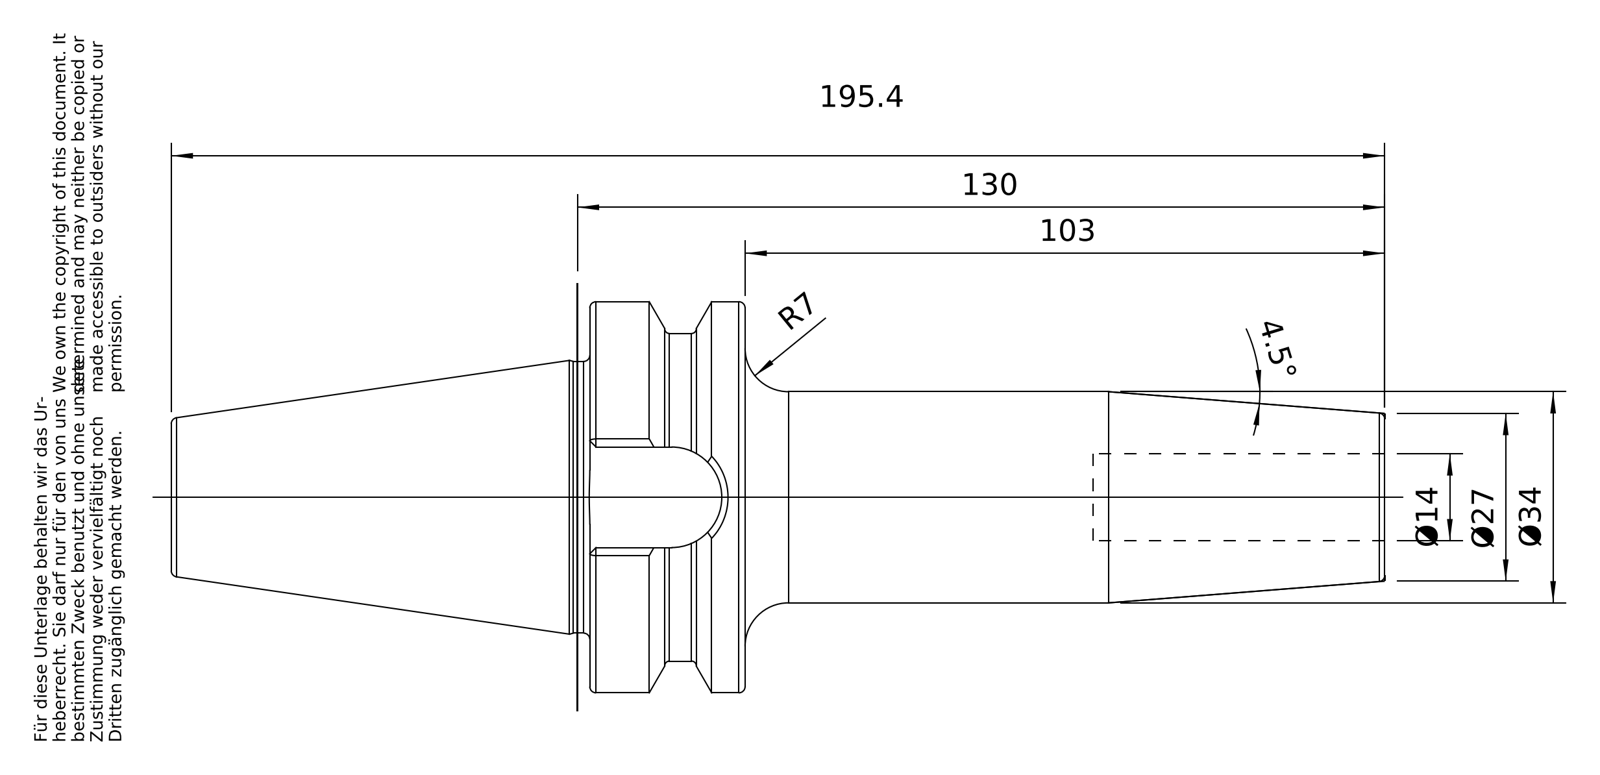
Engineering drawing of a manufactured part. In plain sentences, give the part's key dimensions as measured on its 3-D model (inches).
The part is named "40-644-14". Its 3-D file was written by "PRO/ENGINEER BY PARAMETRIC TECHNOLOGY CORPORATION, 2010430 (CONFIG_CONTROL_DESIGN)". It is 1 solid with 96 faces: 26 planar, 22 cylindrical and 48 other. Overall it measures 7.693 by 2.48 by 2.48 inches. Its volume is 12.56 cubic inches and its surface area 52.33 square inches. Round holes: 1 of diameter 0.545, 1 of diameter 0.551, 1 of diameter 0.67, 1 of diameter 0.689. Round bosses or shafts: 1 of diameter 2.48, 1 of diameter 2.077, 1 of diameter 1.722, 1 of diameter 1.339, 1 of diameter 0.63. Partial cylindrical surfaces (rounded edges, fillets, slot ends): 1 of radius 0.319. The main face-to-face distances are 0.984, 5.039, 4.055, 1.768, 3.189, 2.205, 1.85, 0.638, 2.654, 3.638.
